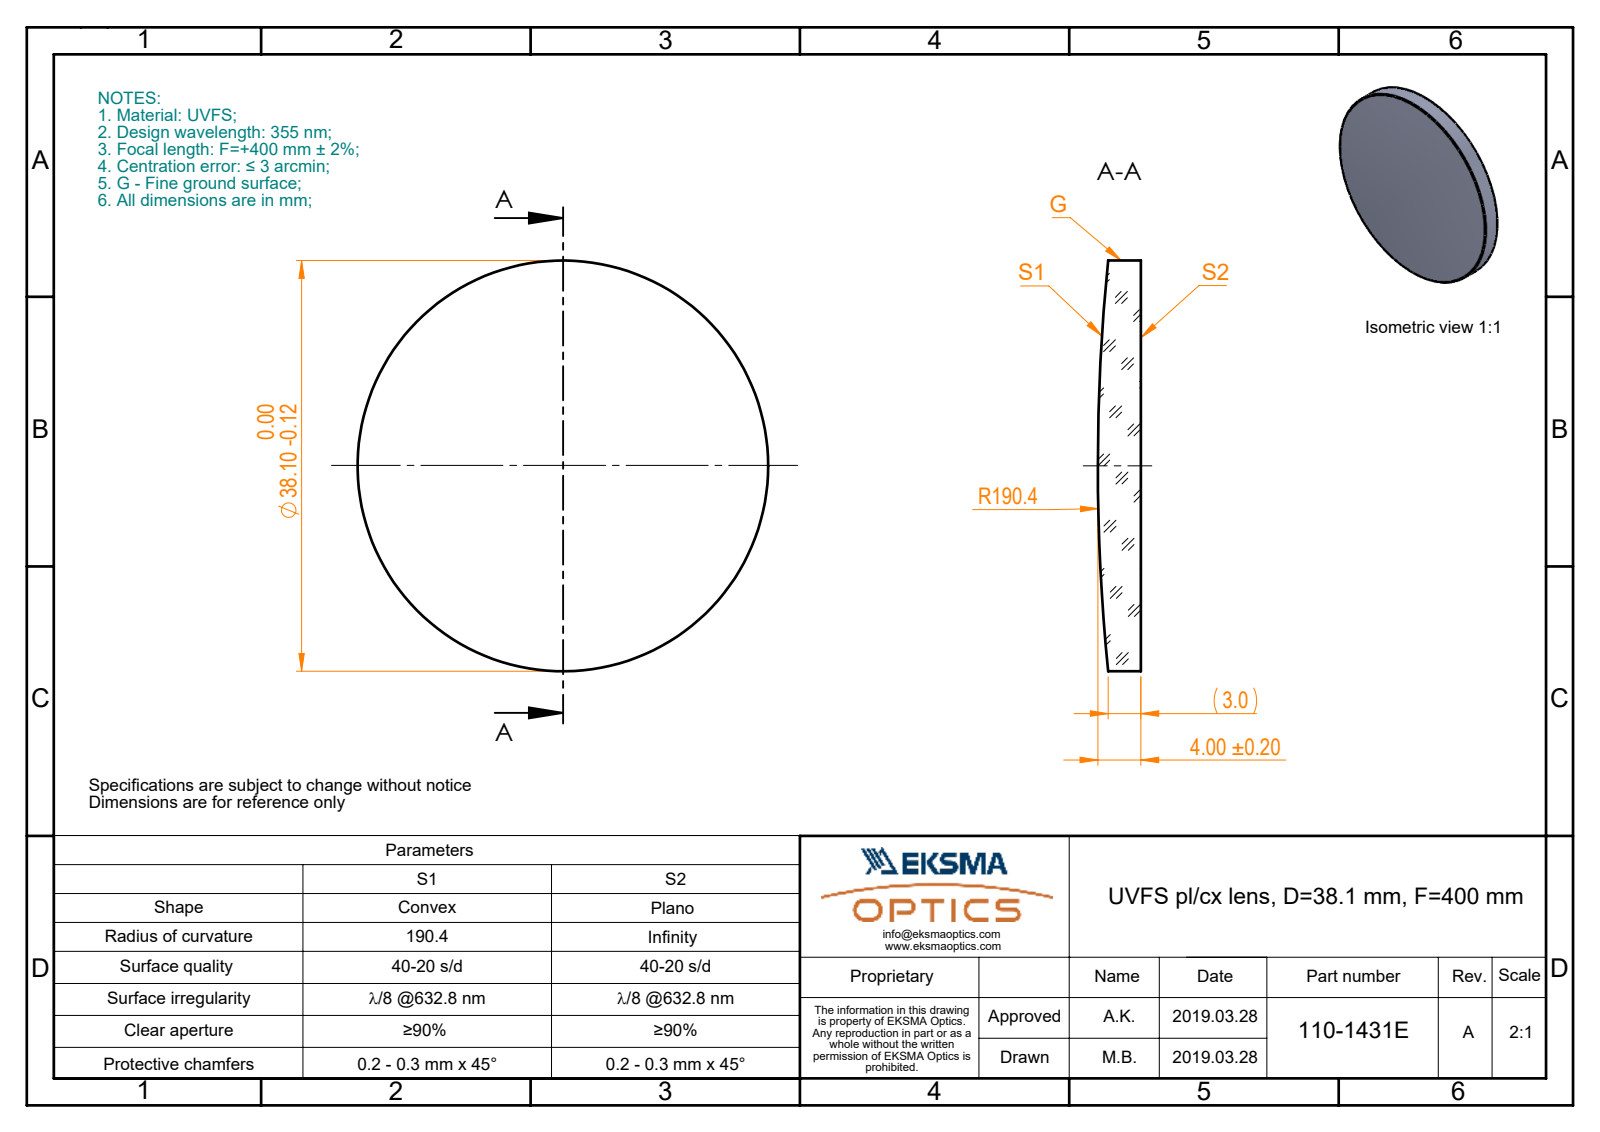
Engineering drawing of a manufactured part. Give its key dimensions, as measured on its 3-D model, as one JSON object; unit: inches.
{"part_name": "110-1431E UVFS pl-cx 38.1 F400", "step_written_by": "SolidWorks 2017 (CONFIG_CONTROL_DESIGN)", "units": "inches", "bodies": {"solids": 1, "faces": 5, "planar": 1, "cylindrical": 2, "other": 2}, "overall_size": [1.5, 1.5, 0.157], "volume_in3": 0.245, "surface_area_in2": 4.103, "round_bosses_or_shafts": [[1.5, 1]]}
